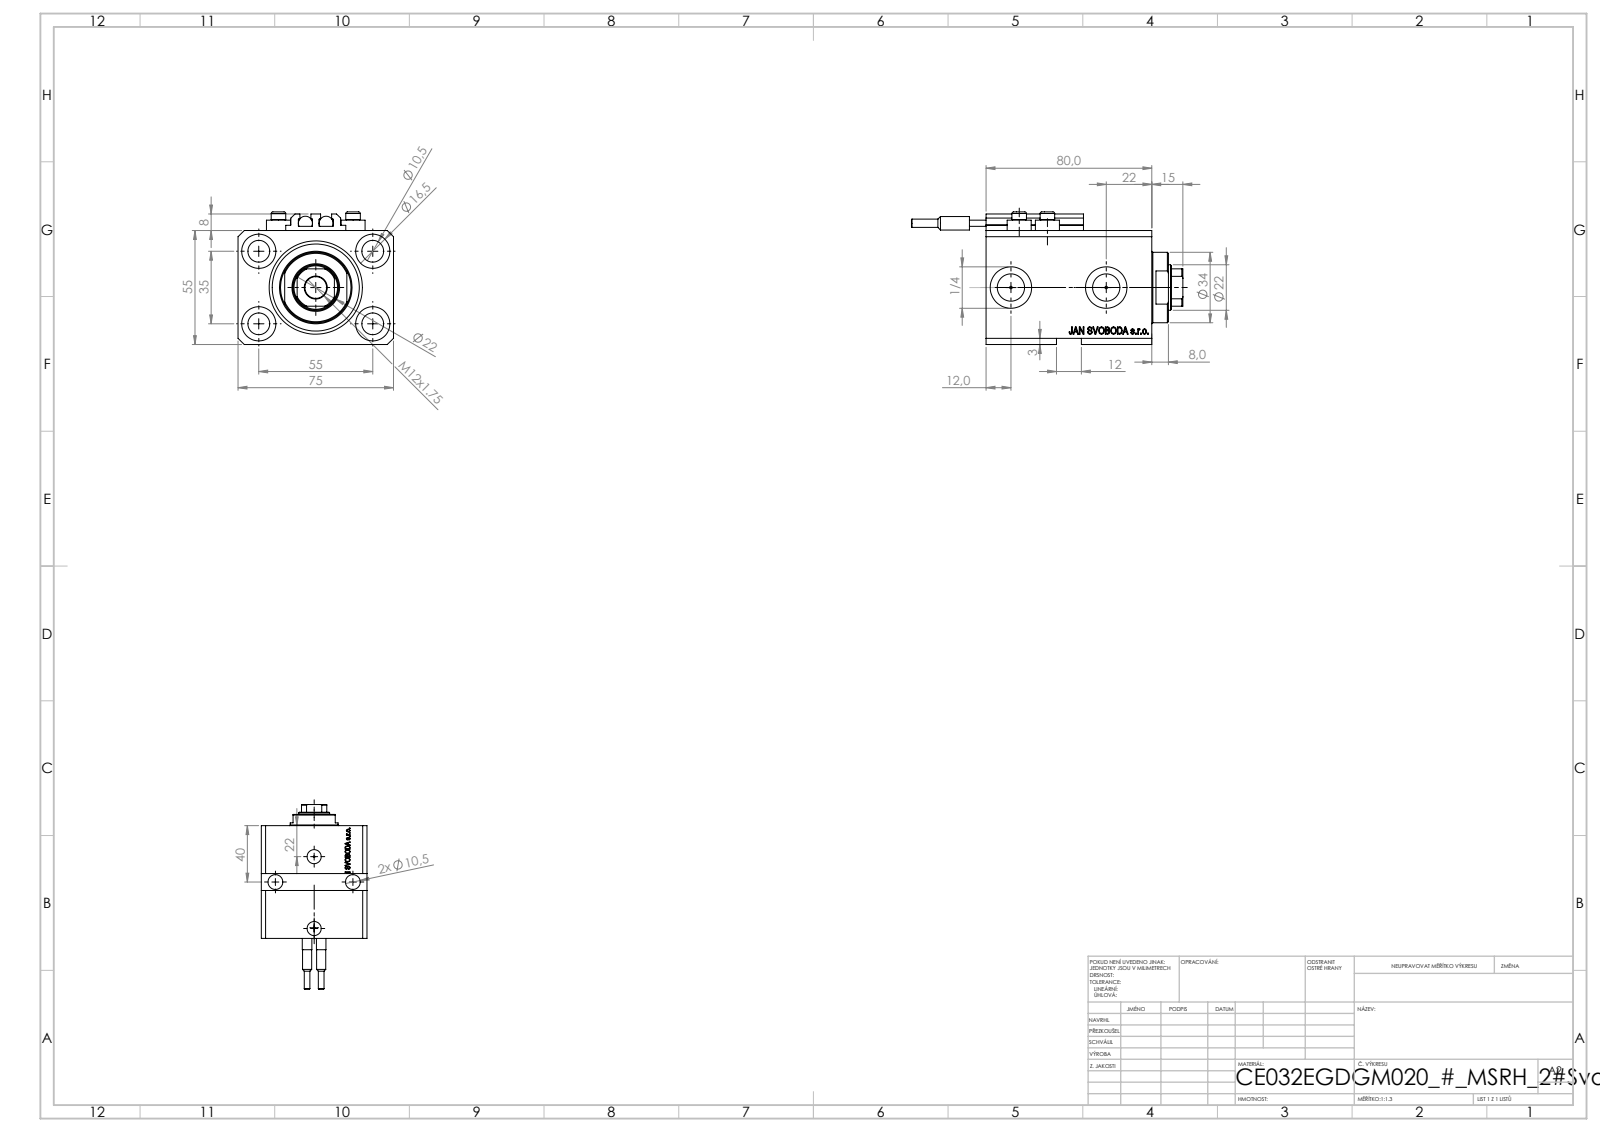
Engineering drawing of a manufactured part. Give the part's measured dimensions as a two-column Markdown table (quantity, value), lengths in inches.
| quantity | value |
| --- | --- |
| part name | V250CE_VC_E; SWITCH_V250CE; V250CE_C_VCP; V250CE_E_Body (+1 more) |
| STEP written by | SolidWorks 2019 (CONFIG_CONTROL_DESIGN) |
| units | inches |
| bodies | 10 solids, 1132 faces (550 planar, 150 cylindrical, 432 other) |
| overall size | 5.157 × 2.953 × 2.52 |
| volume | 17.32 in³ |
| surface area | 121.5 in² |
| round holes (diameter × count) | 0.413 × 7, 0.049 × 4, 0.157 × 4, 0.65 × 4, 0.394 × 2, 0.518 × 2, 0.787 × 2, 0.866 × 1, 1.26 × 1, 1.772 × 1 |
| round bosses / shafts (diameter × count) | 0.457 × 4, 0.276 × 4, 0.268 × 2, 0.256 × 2, 0.157 × 2, 1.339 × 1 |
| partial cylindrical surfaces (radius × count) | 0.008 × 10, 0.413 × 1 |
| main face-to-face distances | 2.165, 2.953, 0.591, 0.118, 3.15, 2.559, 0.39, 2.169, 2.244, 2.76 |
| hole center spacings | 1.283, 2.165, 0.535, 0.555, 0.783, 0.792, 1.016, 1.121 |
